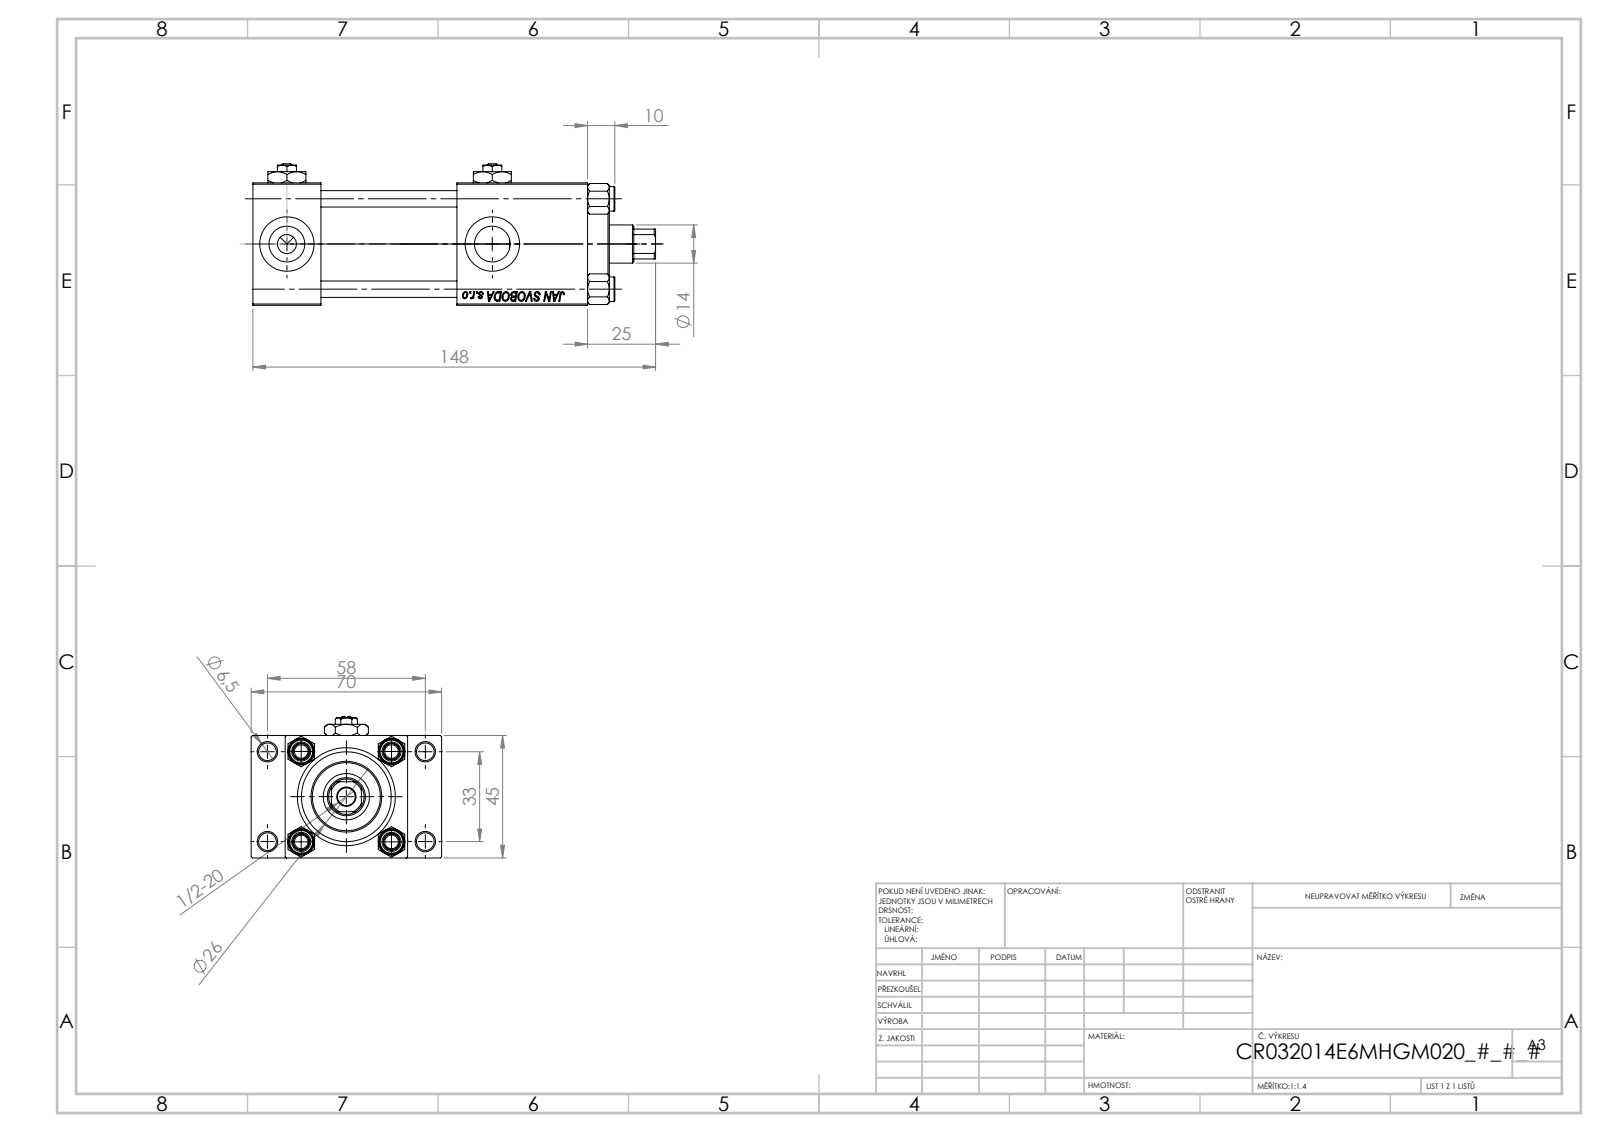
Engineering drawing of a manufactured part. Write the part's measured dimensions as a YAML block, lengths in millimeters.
part_name: "V215_VC_A; NUT_M5_E; V215CR_E_Body; Zatka_pro_OIL_PORT (+2 more)"
step_written_by: "SolidWorks 2019 (CONFIG_CONTROL_DESIGN)"
units: millimeters
bodies: {solids: 13, faces: 1235, planar: 544, cylindrical: 97, other: 594}
overall_size: [148, 70, 52]
volume: 217794
surface_area: 78247
round_holes:
  - {diameter: 6.5, count: 5}
  - {diameter: 6, count: 4}
  - {diameter: 13.16, count: 4}
  - {diameter: 20, count: 4}
  - {diameter: 7, count: 3}
  - {diameter: 14, count: 1}
  - {diameter: 17, count: 1}
  - {diameter: 24, count: 1}
  - {diameter: 32, count: 1}
  - {diameter: 33, count: 1}
round_bosses_or_shafts:
  - {diameter: 9, count: 4}
  - {diameter: 38, count: 1}
  - {diameter: 26, count: 1}
partial_cylinders:
  - {radius: 6.5, count: 1}
face_to_face_distances: [45, 25, 12.5, 57.5, 123, 98, 50, 75, 48, 94.3]
hole_center_spacings: [12.4, 23.48, 33.2, 33.37, 35.35, 45.6, 56.35, 33]
